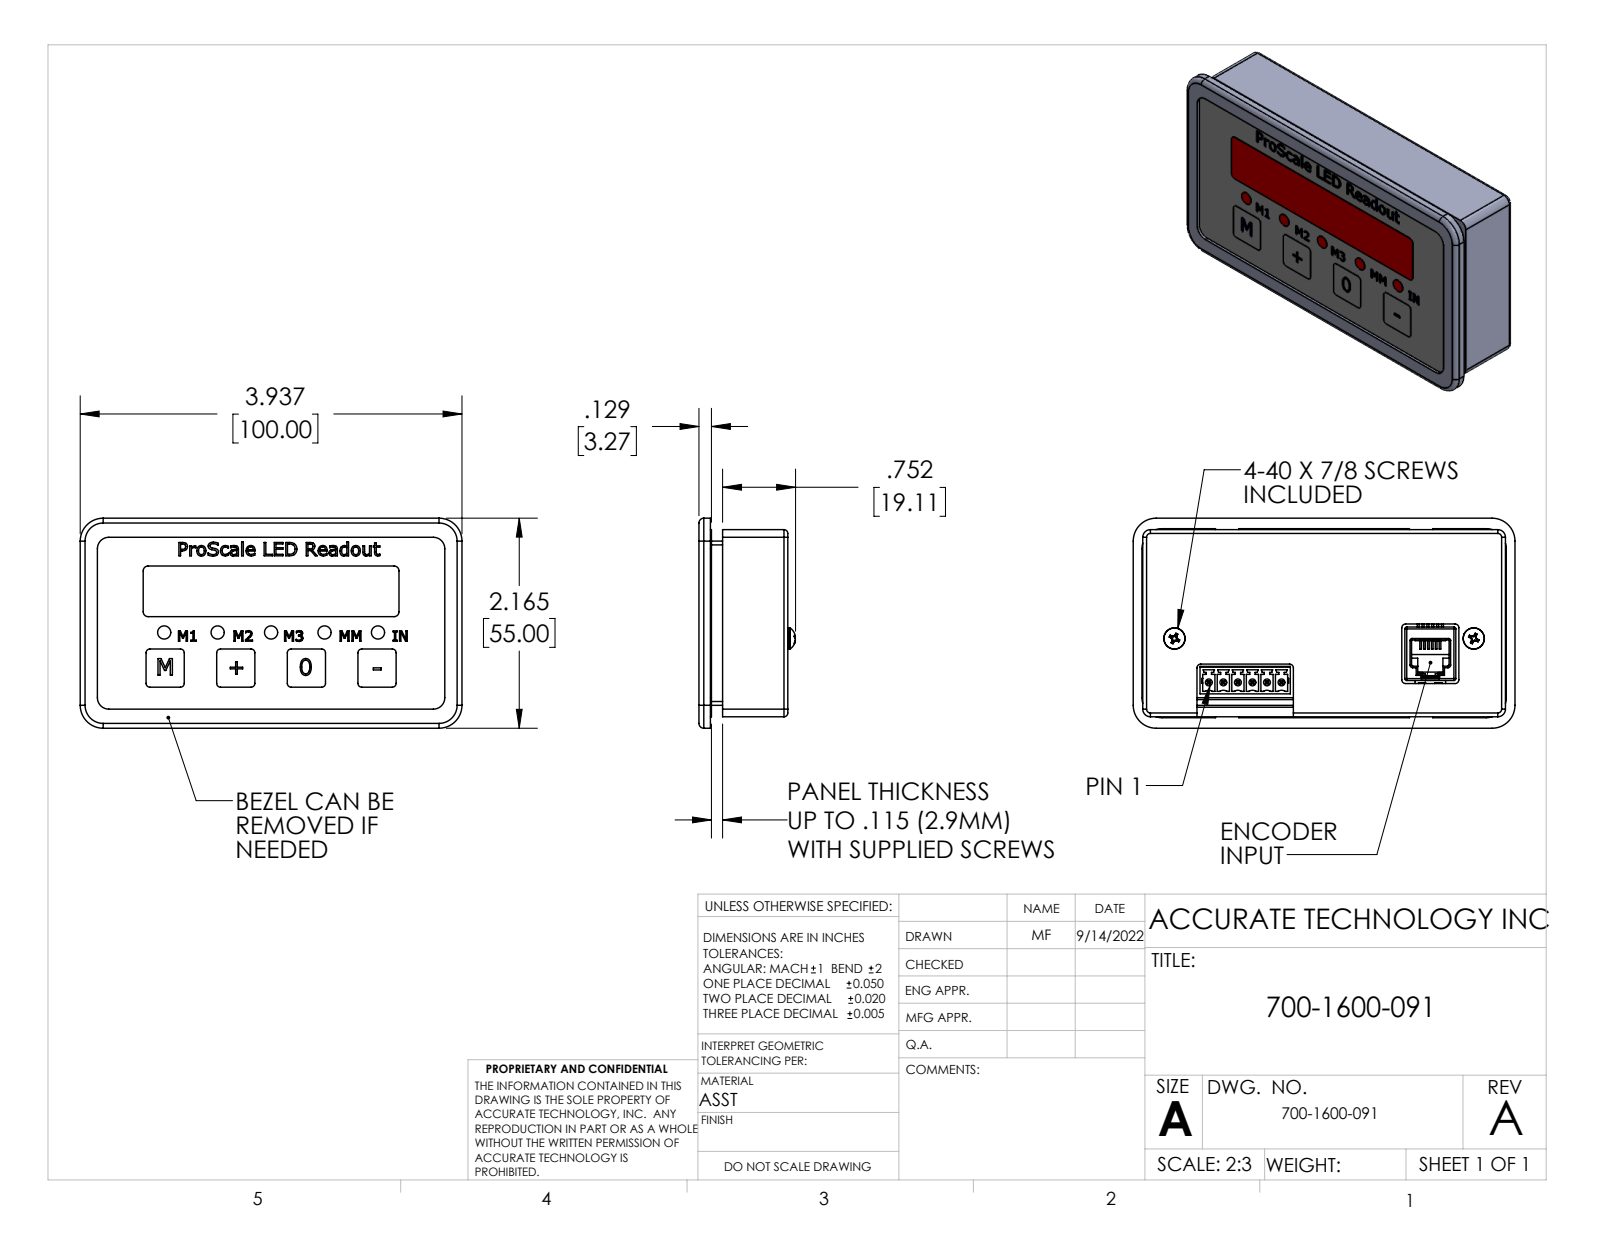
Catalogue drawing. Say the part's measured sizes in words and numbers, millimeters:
The part is named "700-1600-091; CUI_DEVICES_TBP02R2-381-06GR_header; c-1-338086-6-aa_6p plug; 92395A112_Brass Screw-to-Expand Inserts (+8 more)". Its 3-D file was written by "SolidWorks 2022 (AUTOMOTIVE_DESIGN)". It is 31 solids with 4530 faces: 1557 planar, 937 cylindrical and 2036 other. Overall it measures 100 by 55 by 25.2 millimeters. Its volume is 45 640 cubic millimeters and its surface area 61 190 square millimeters. Round holes: 6 of diameter 3, 5 of diameter 3.5, 4 of diameter 2.3, 2 of diameter 3.3, 2 of diameter 4. Round bosses or shafts: 6 of diameter 5.6, 6 of diameter 1.8, 4 of diameter 4.1, 4 of diameter 1.7, 2 of diameter 6.4, 2 of diameter 5.5, 2 of diameter 4.2, 2 of diameter 2.8. Partial cylindrical surfaces (rounded edges, fillets, slot ends): 36 of radius 0.3, 35 of radius 0.2, 34 of radius 1, 25 of radius 0.5, 22 of radius 0.1, 12 of radius 0.5, 9 of radius 0.4, 8 of radius 0.2. The main face-to-face distances are 2, 4.8, 5.3, 2.5, 3, 0.5, 17.2, 22, 22.5, 15.6. The hole center spacings are 14, 28, 11.3, 12, 17.5, 20, 21.4, 25.2.
